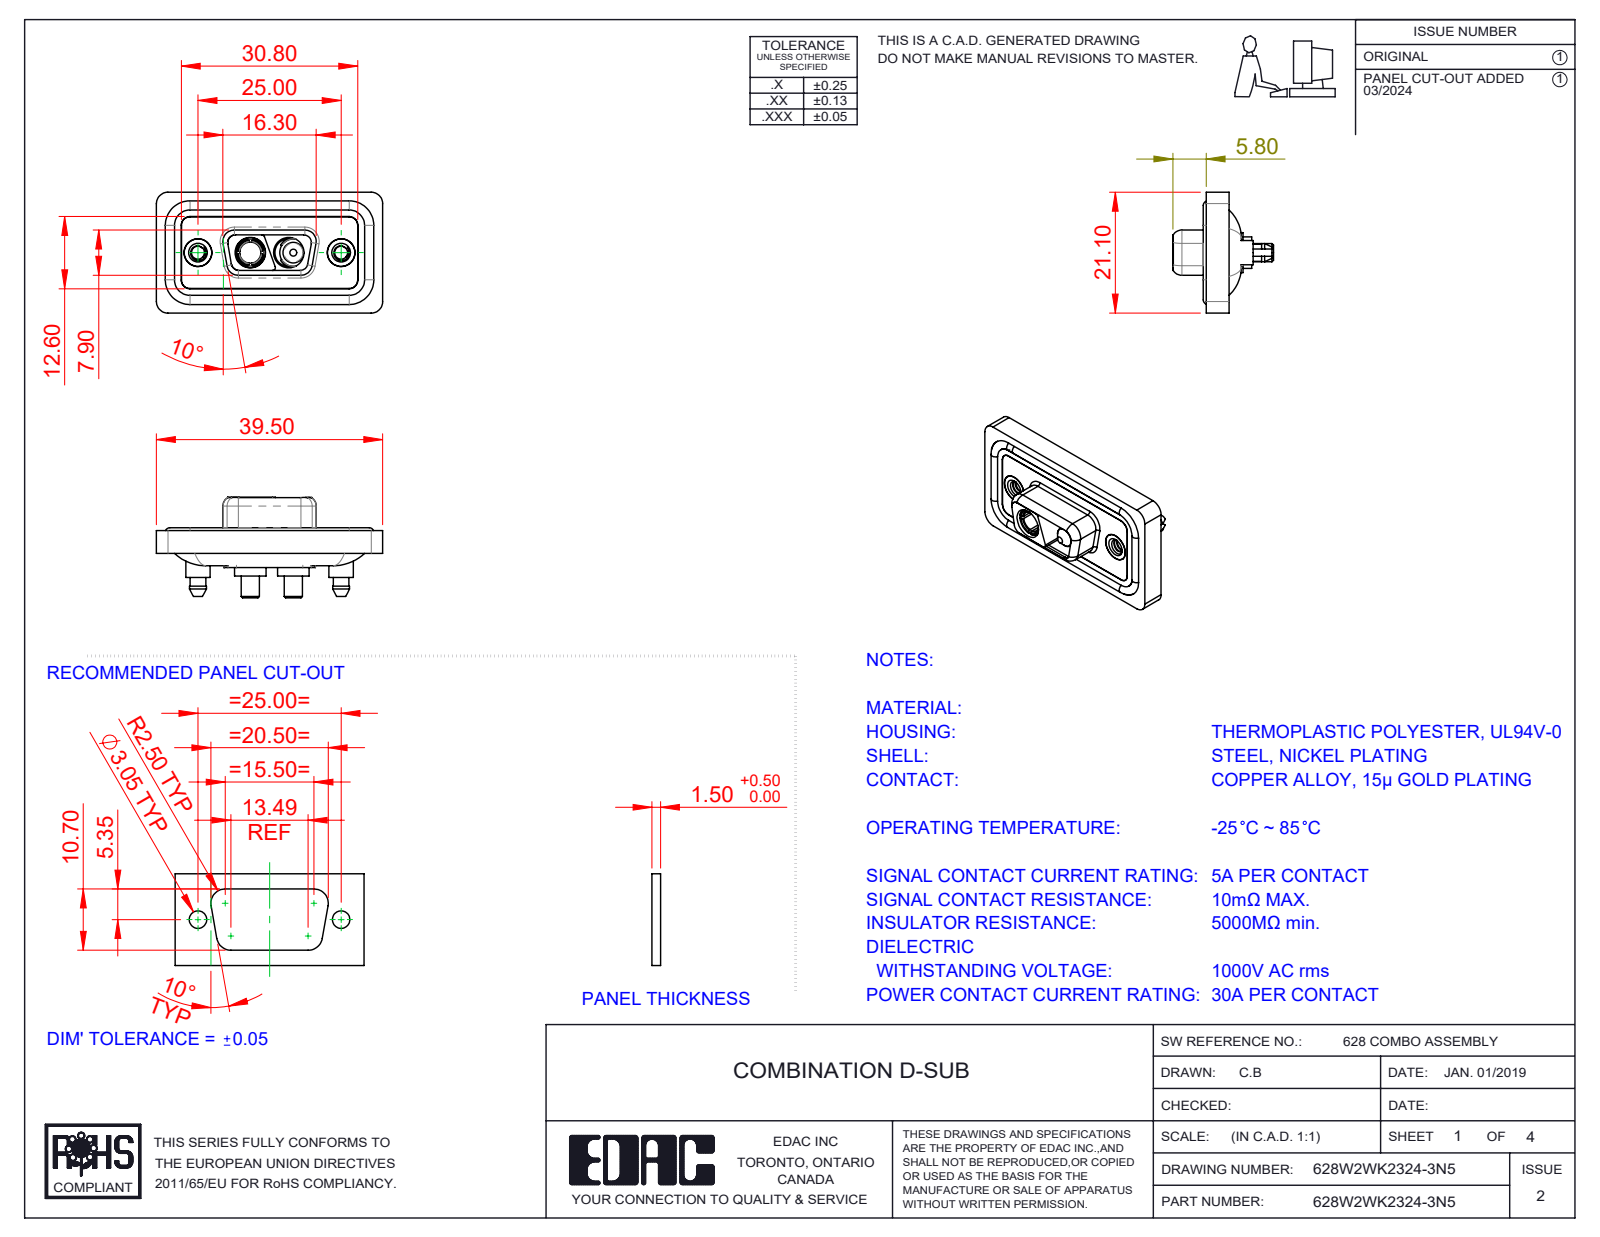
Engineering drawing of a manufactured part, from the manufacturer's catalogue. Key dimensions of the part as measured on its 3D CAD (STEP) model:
Part name (STEP PRODUCT): 628Combo Shell Front_09 Contacts; 628Combo Housing_2WK2; 628Combo Shell Rear_09 Contacts; Power Socket_30A S (+4 more)
STEP written by: SolidWorks 2023 (CONFIG_CONTROL_DESIGN)
Units: millimetres
Bodies: 11 solids, 550 faces (160 planar, 263 cylindrical, 127 other)
Overall size (bounding box): 39.5 × 21.1 × 17.55
Volume: 4 751 mm³ · Surface area: 7 686 mm²
Round holes (diameter × count): ⌀4.85 ×4, ⌀2.26 ×2, ⌀4 ×2, ⌀4.05 ×2, ⌀5 ×2, ⌀5.3 ×2, ⌀3.7 ×1
Round bosses / shafts (diameter × count): ⌀1.6 ×4, ⌀5.5 ×2, ⌀5.4 ×2, ⌀5.2 ×2, ⌀4.95 ×2, ⌀4.8 ×2, ⌀4.75 ×2, ⌀4.25 ×2
Partial cylindrical surfaces — rounded edges, fillets, slot ends (radius × count): R1.5 ×24, R2 ×18, R1.6 ×10, R1.35 ×8, R0.5 ×6, R0.25 ×4, R0.6 ×4, R0.65 ×4
Main face-to-face distances: 0.4, 1.1, 2.9, 1.6, 0.5, 1.8, 5.65, 1.5, 4, 5.35
Hole centre spacings: 9.14, 15.86, 6.72, 25
